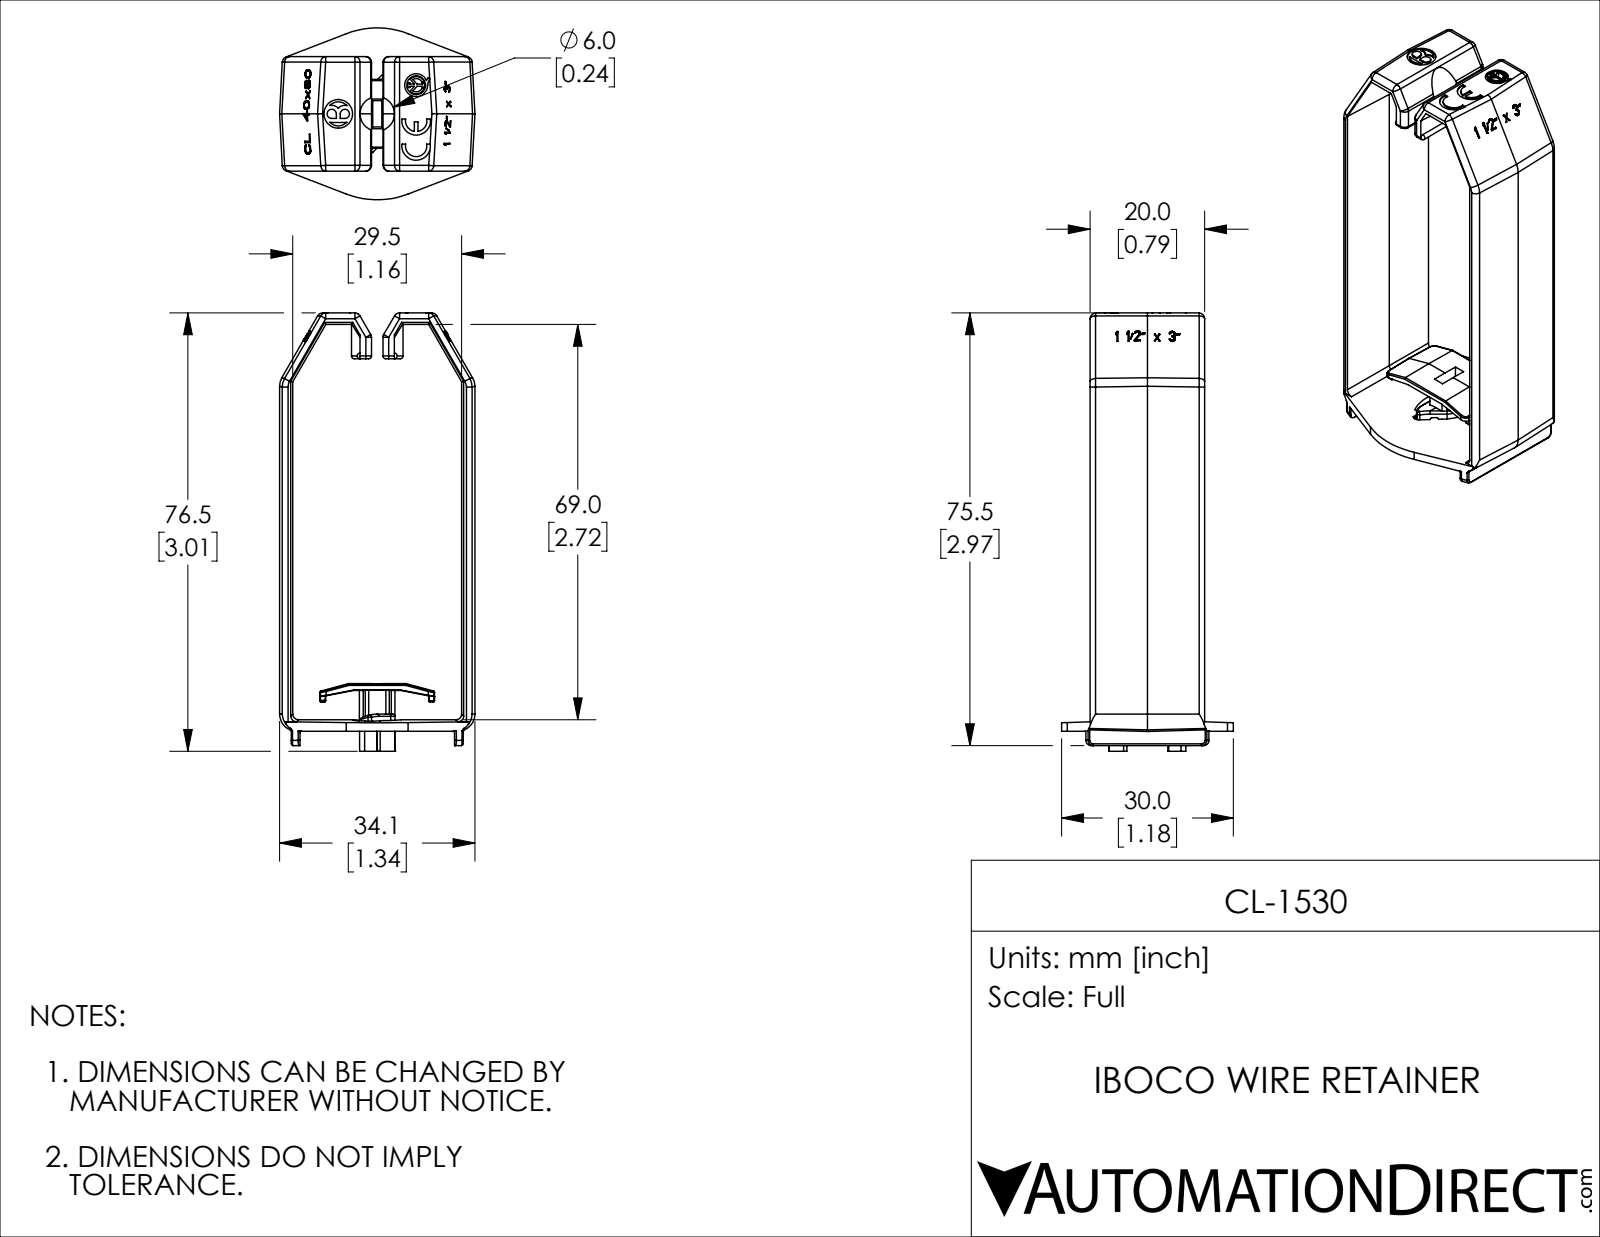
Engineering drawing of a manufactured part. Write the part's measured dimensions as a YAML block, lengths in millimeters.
part_name: "CL-1530"
step_written_by: "SolidWorks 2019 (CONFIG_CONTROL_DESIGN)"
units: millimeters
bodies: {solids: 1, faces: 803, planar: 565, cylindrical: 180, other: 58}
overall_size: [76.5, 34.1, 30]
volume: 8060
surface_area: 10120
round_holes:
  - {diameter: 4, count: 1}
  - {diameter: 5, count: 1}
round_bosses_or_shafts:
  - {diameter: 3.3, count: 1}
partial_cylinders:
  - {radius: 1, count: 36}
  - {radius: 0.2, count: 22}
  - {radius: 0.3, count: 14}
  - {radius: 0.5, count: 12}
  - {radius: 3, count: 9}
  - {radius: 0.4, count: 6}
  - {radius: 0.9, count: 6}
  - {radius: 2.5, count: 4}
face_to_face_distances: [29.5, 34.1, 68.9, 73, 2, 4, 16, 1.5, 20, 12]
hole_center_spacings: [14.5]
